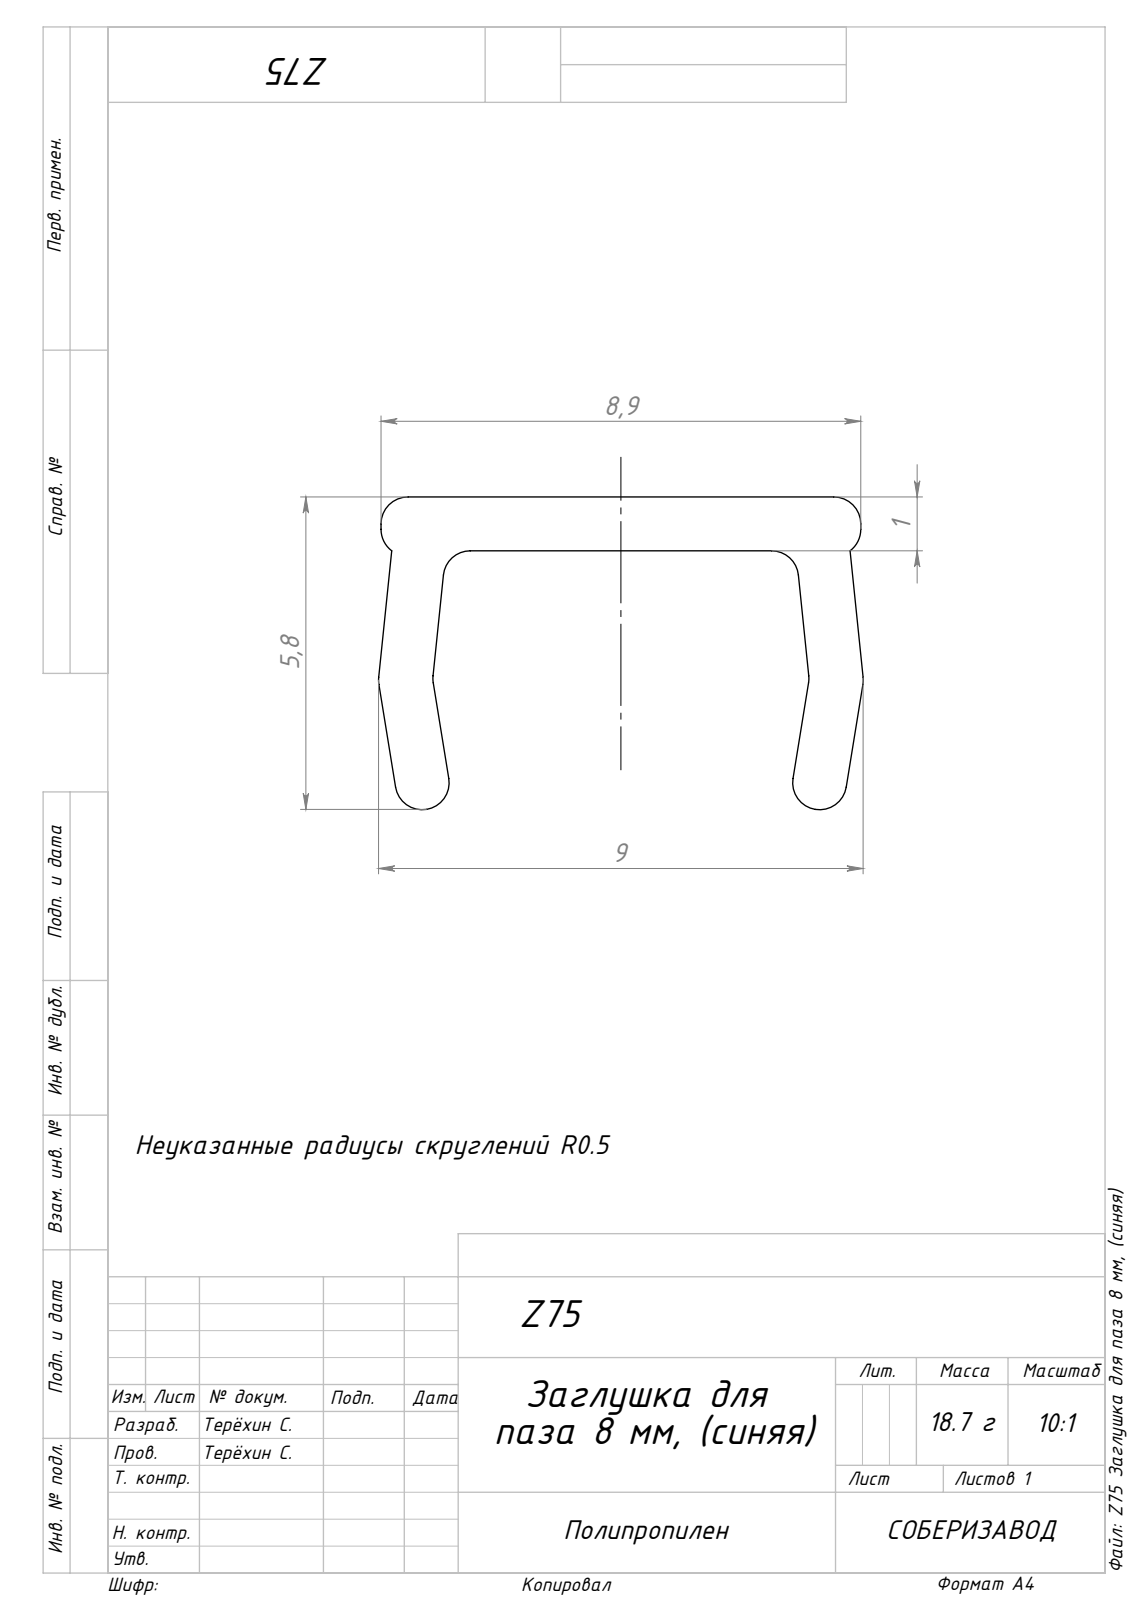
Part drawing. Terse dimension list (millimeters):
name: Z75 Заглушка для паза 8 мм, (синяя); Z75 Заглушка для паза 8 мм, (синяя)_00
written by: SolidWorks 2026 (CONFIG_CONTROL_DESIGN)
unit: mm
bodies: 1 solid, 30 faces (14 planar, 16 cylindrical, 0 other)
size: 1000 × 8.99 × 5.81
volume: 18 303 mm³; area: 37 304 mm²
rounds: 12× R0.5
face distances: 1, 8.9, 1000
